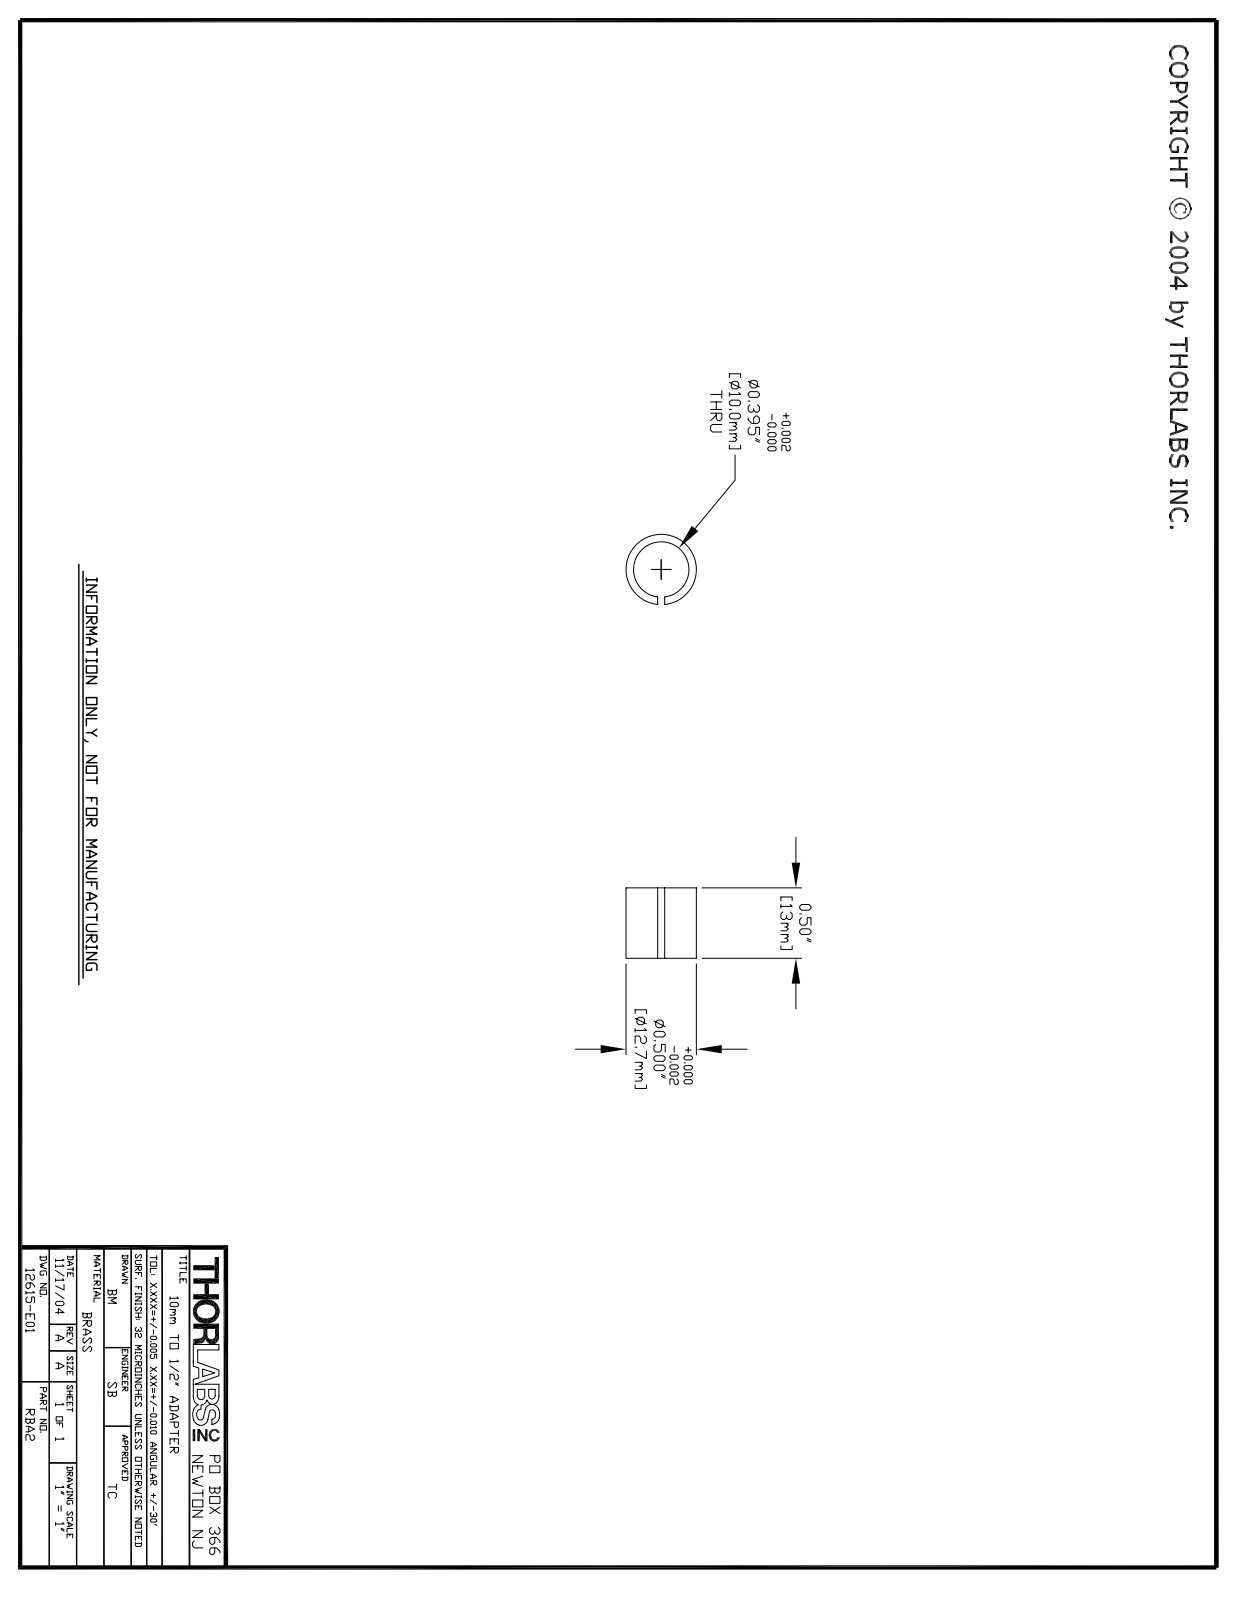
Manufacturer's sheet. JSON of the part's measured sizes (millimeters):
{"part_name": "12615-E0W", "step_written_by": "SolidWorks 2011 (CONFIG_CONTROL_DESIGN)", "units": "millimeters", "bodies": {"solids": 1, "faces": 10, "planar": 4, "cylindrical": 6, "other": 0}, "overall_size": [12.7, 12.7, 12.6], "volume_mm3": 570, "surface_area_mm2": 998, "round_holes": [[10, 1]], "round_bosses_or_shafts": [[12.7, 1]], "face_to_face_distances": [12.7, 1.3]}
